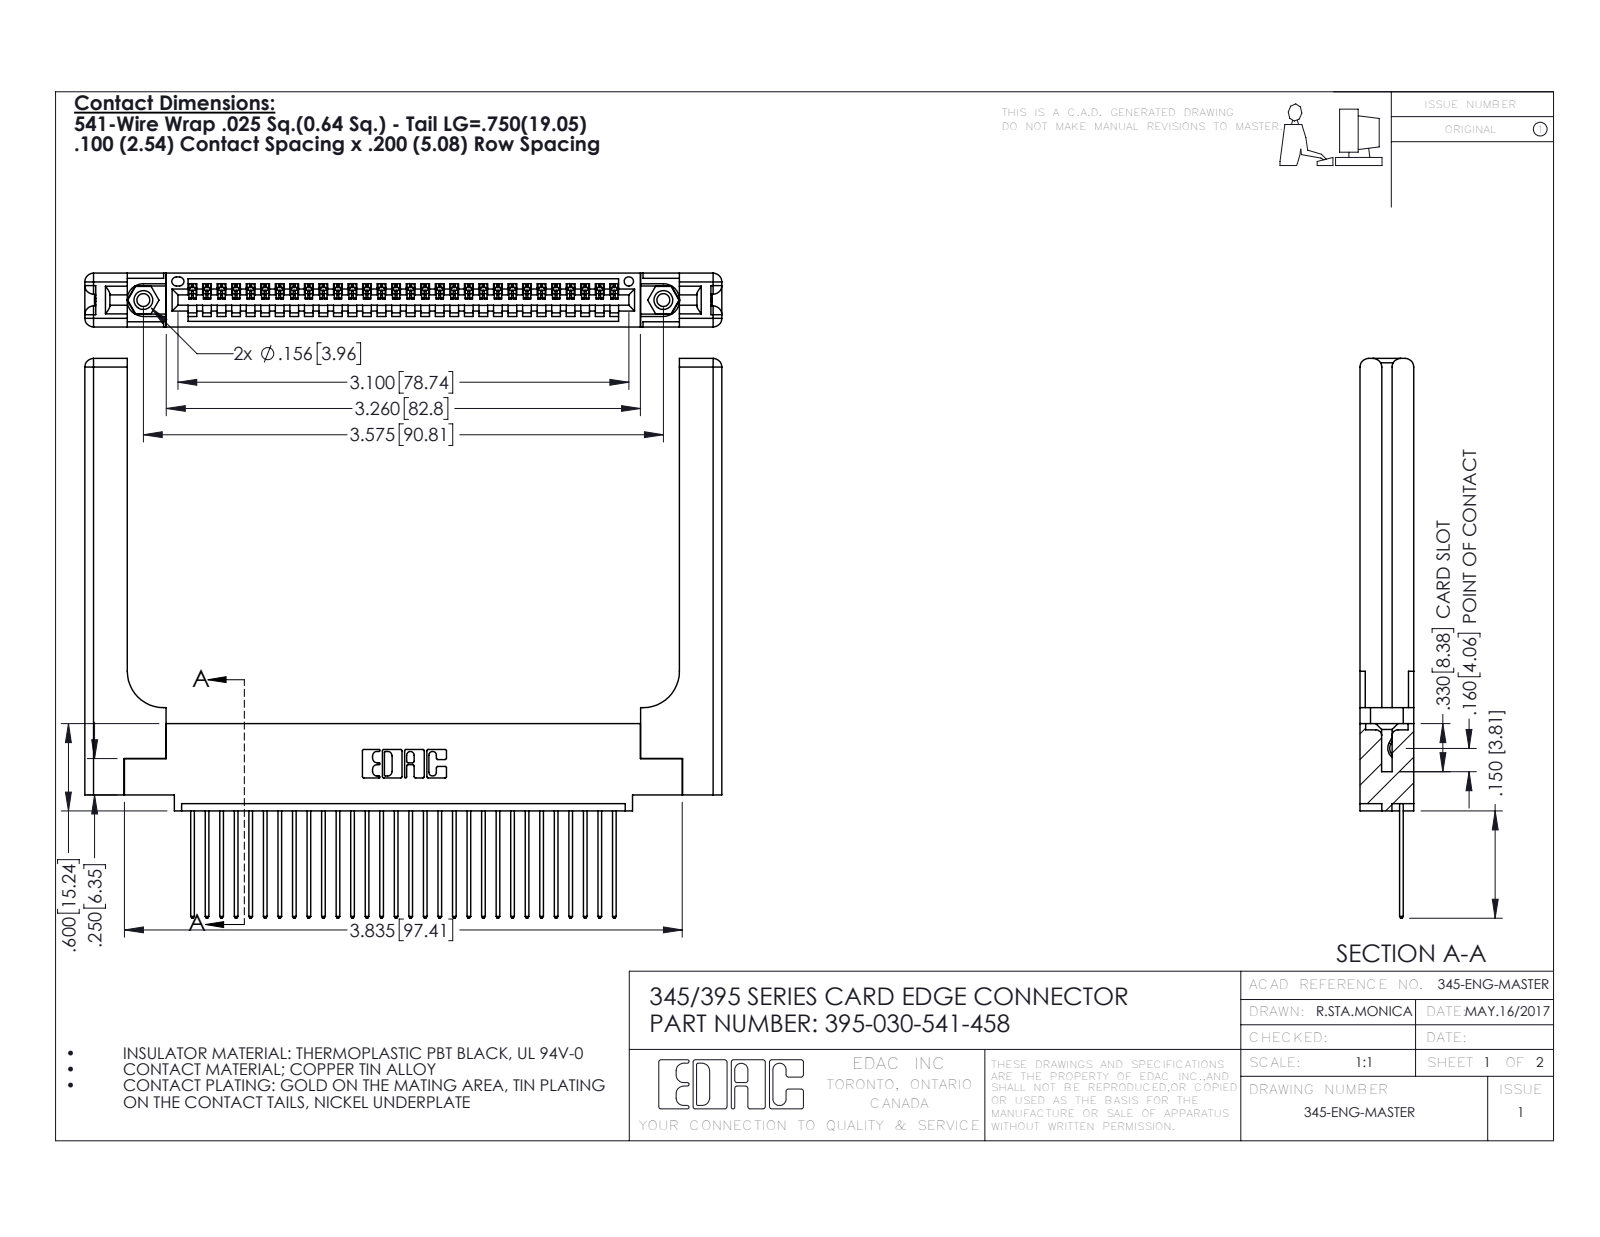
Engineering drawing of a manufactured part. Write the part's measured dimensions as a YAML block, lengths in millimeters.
part_name: "345-250-001_345-250-001-102; 345-292-001_345-293-141; 345 Part_0.110 Offset - 0.156 Dia-TH; 395-030-541-458 (+1 more)"
step_written_by: "SolidWorks 2016 (CONFIG_CONTROL_DESIGN)"
units: millimeters
bodies: {solids: 35, faces: 2126, planar: 1432, cylindrical: 634, other: 60}
overall_size: [111.2, 97.7, 9.4]
volume: 18990
surface_area: 19750
round_holes:
  - {diameter: 2.3, count: 2}
  - {diameter: 3.2, count: 2}
  - {diameter: 4, count: 2}
  - {diameter: 1.6, count: 1}
round_bosses_or_shafts:
  - {diameter: 3.9, count: 2}
partial_cylinders:
  - {radius: 0.2, count: 60}
  - {radius: 0.3, count: 60}
  - {radius: 0.3, count: 22}
  - {radius: 1.5, count: 16}
  - {radius: 0.2, count: 6}
  - {radius: 0.8, count: 6}
  - {radius: 0.7, count: 3}
  - {radius: 0.8, count: 2}
face_to_face_distances: [9.4, 1.8, 7.6, 2.5, 6.9, 0.6, 5.1, 3.8, 3.8, 2]
hole_center_spacings: [6.9, 84.8, 90.8]
